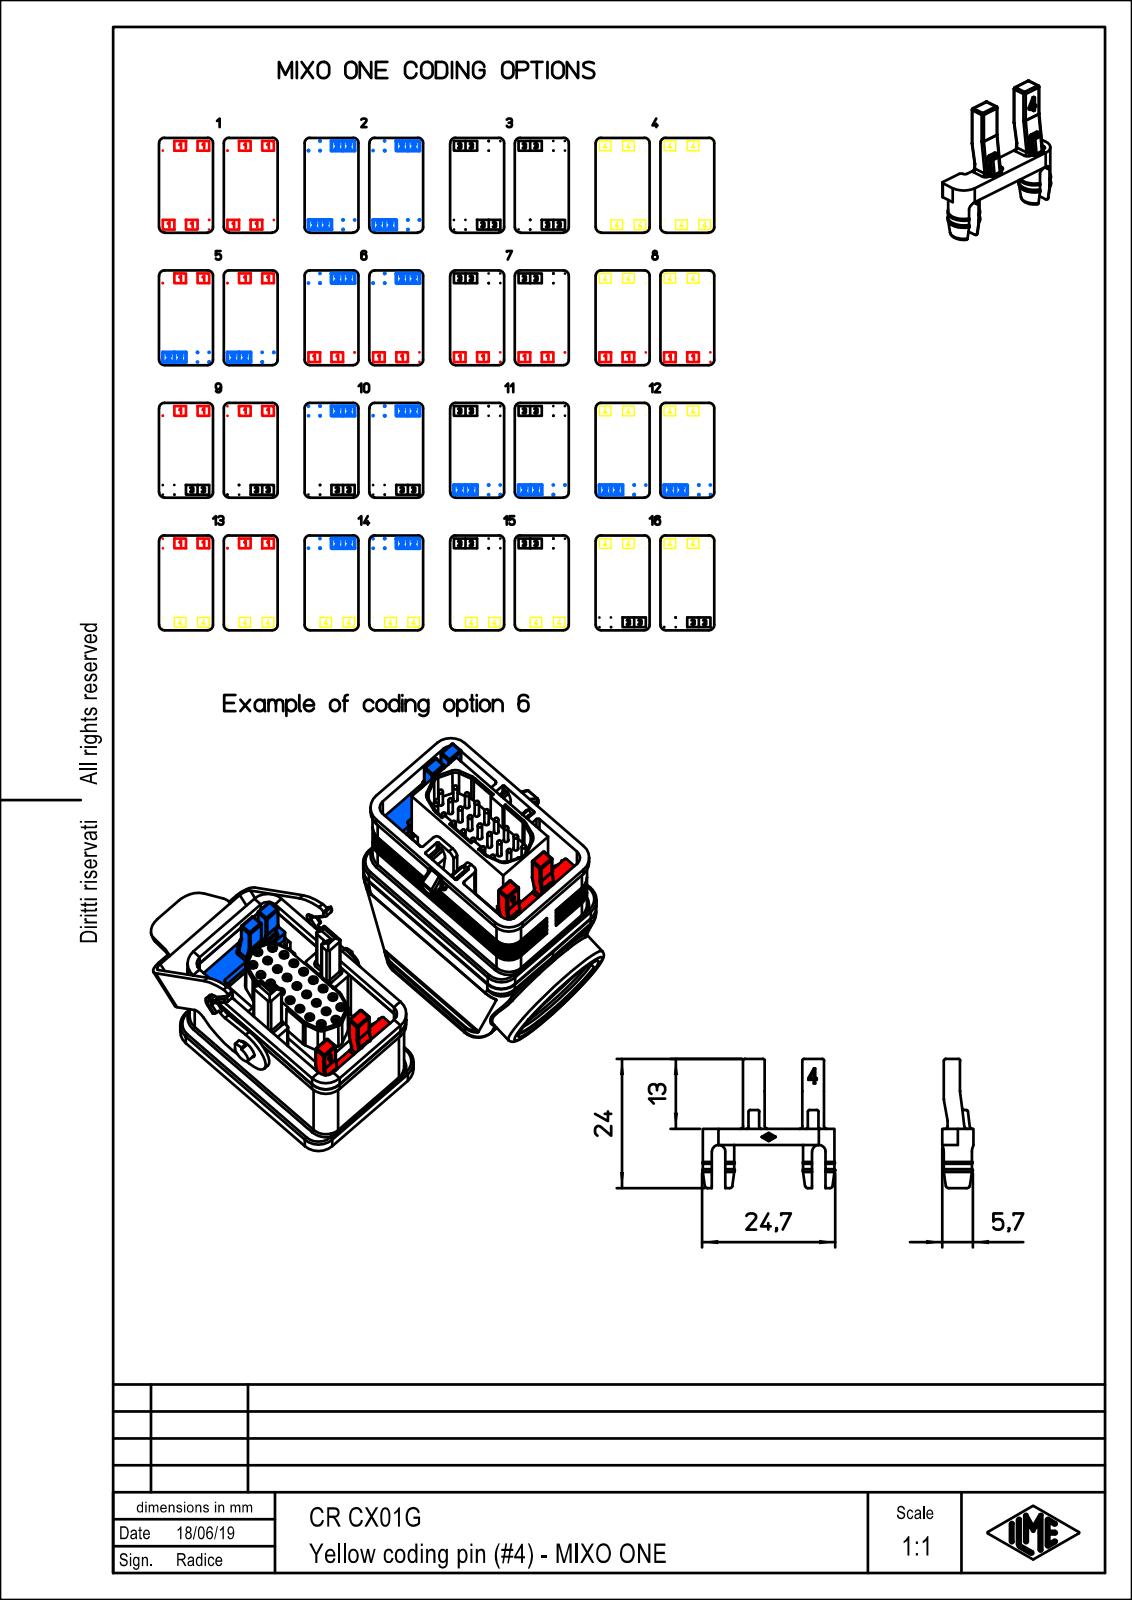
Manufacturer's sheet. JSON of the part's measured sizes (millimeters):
{"part_name": "CR_CX01G", "step_written_by": "Creo Elements/Direct Modeling 20.1B 02-Apr-2019 (C) Parametric Technology GmbH (AUTOMOTIVE_DESIGN)", "units": "millimeters", "bodies": {"solids": 1, "faces": 50, "planar": 36, "cylindrical": 10, "other": 4}, "overall_size": [24.4, 24, 5.8], "volume_mm3": 878, "surface_area_mm2": 1139, "round_bosses_or_shafts": [[5.8, 2]], "partial_cylinders_radius": [[1.25, 2]], "face_to_face_distances": [3, 2.5, 11, 4, 18.6, 5.8, 3.3, 5.5, 0.7, 4.8]}
